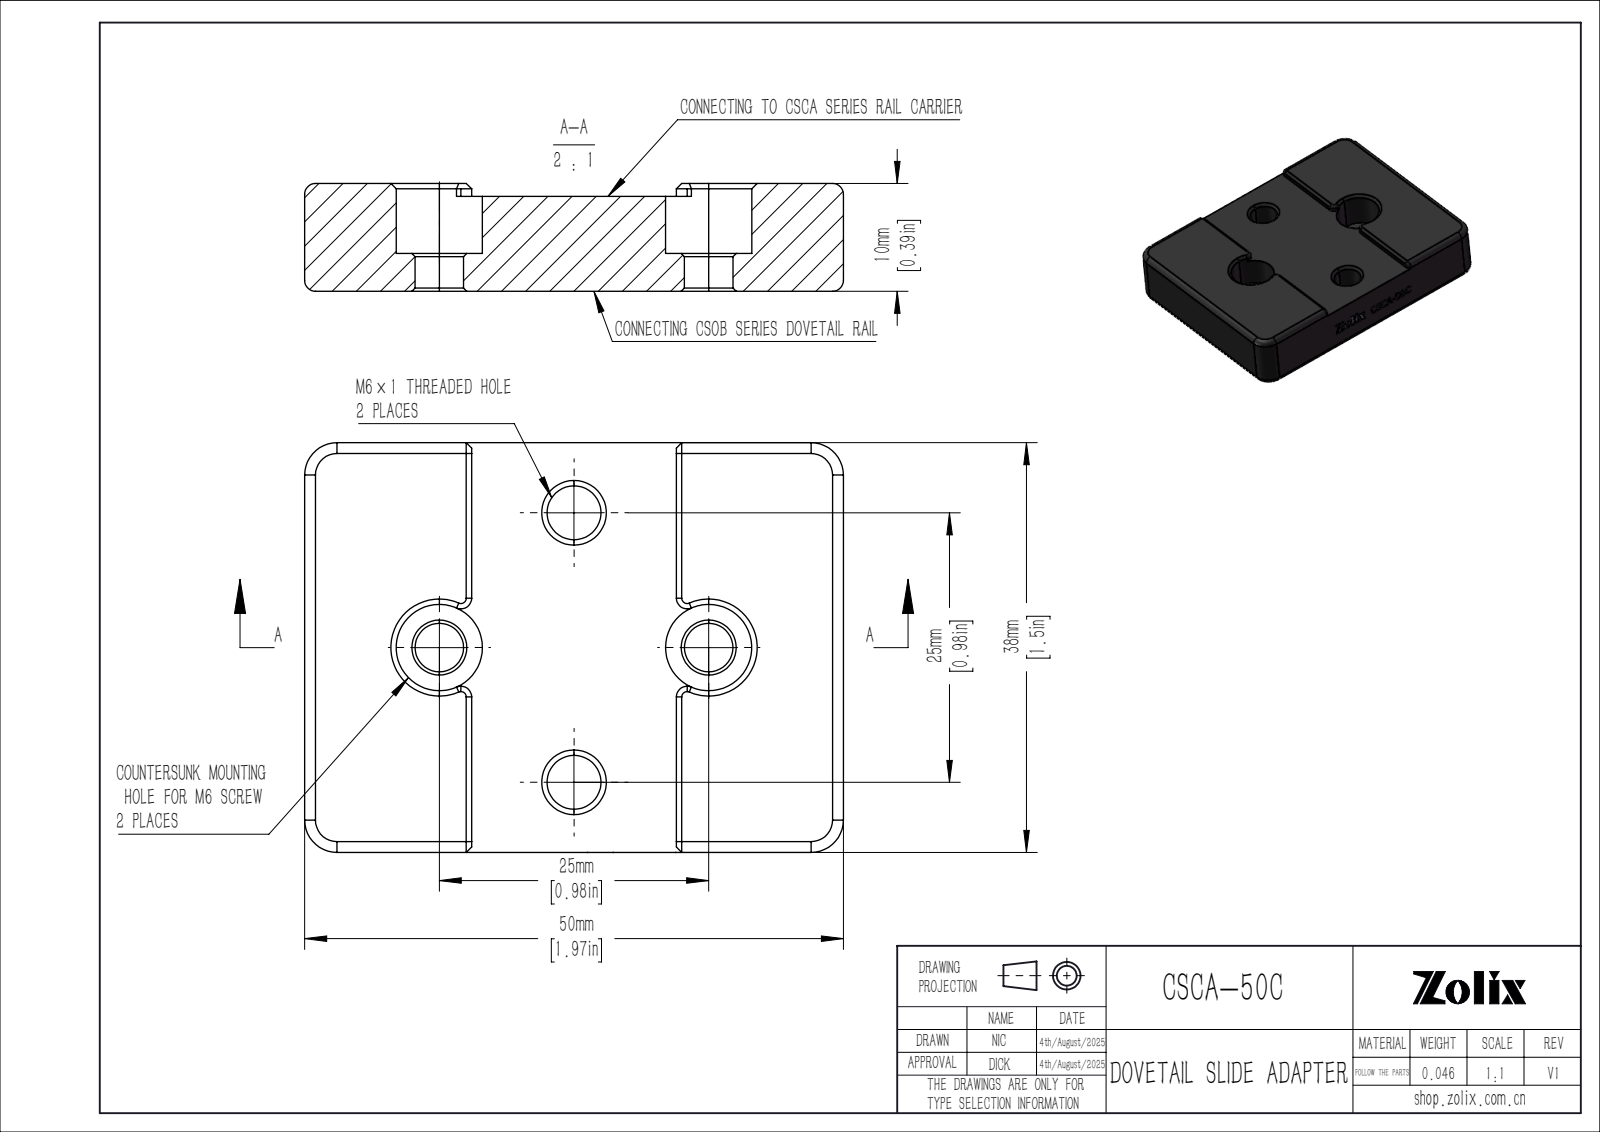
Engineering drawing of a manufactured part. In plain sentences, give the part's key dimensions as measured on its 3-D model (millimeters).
The part is named "CSCA-50C". Its 3-D file was written by "SolidWorks 2020 (CONFIG_CONTROL_DESIGN)". It is 1 solid with 365 faces: 220 planar, 32 cylindrical and 113 other. Overall it measures 50 by 38 by 10 millimeters. Its volume is 16 863 cubic millimeters and its surface area 5 878 square millimeters. Round holes: 2 of diameter 4.5, 2 of diameter 5, 2 of diameter 8. Partial cylindrical surfaces (rounded edges, fillets, slot ends): 12 of radius 1, 4 of radius 3. The main face-to-face distances are 10, 8.8, 1.2, 38, 50, 3.5, 5.3, 6.5, 15.5, 34.5. The hole center spacings are 17.68, 25.
